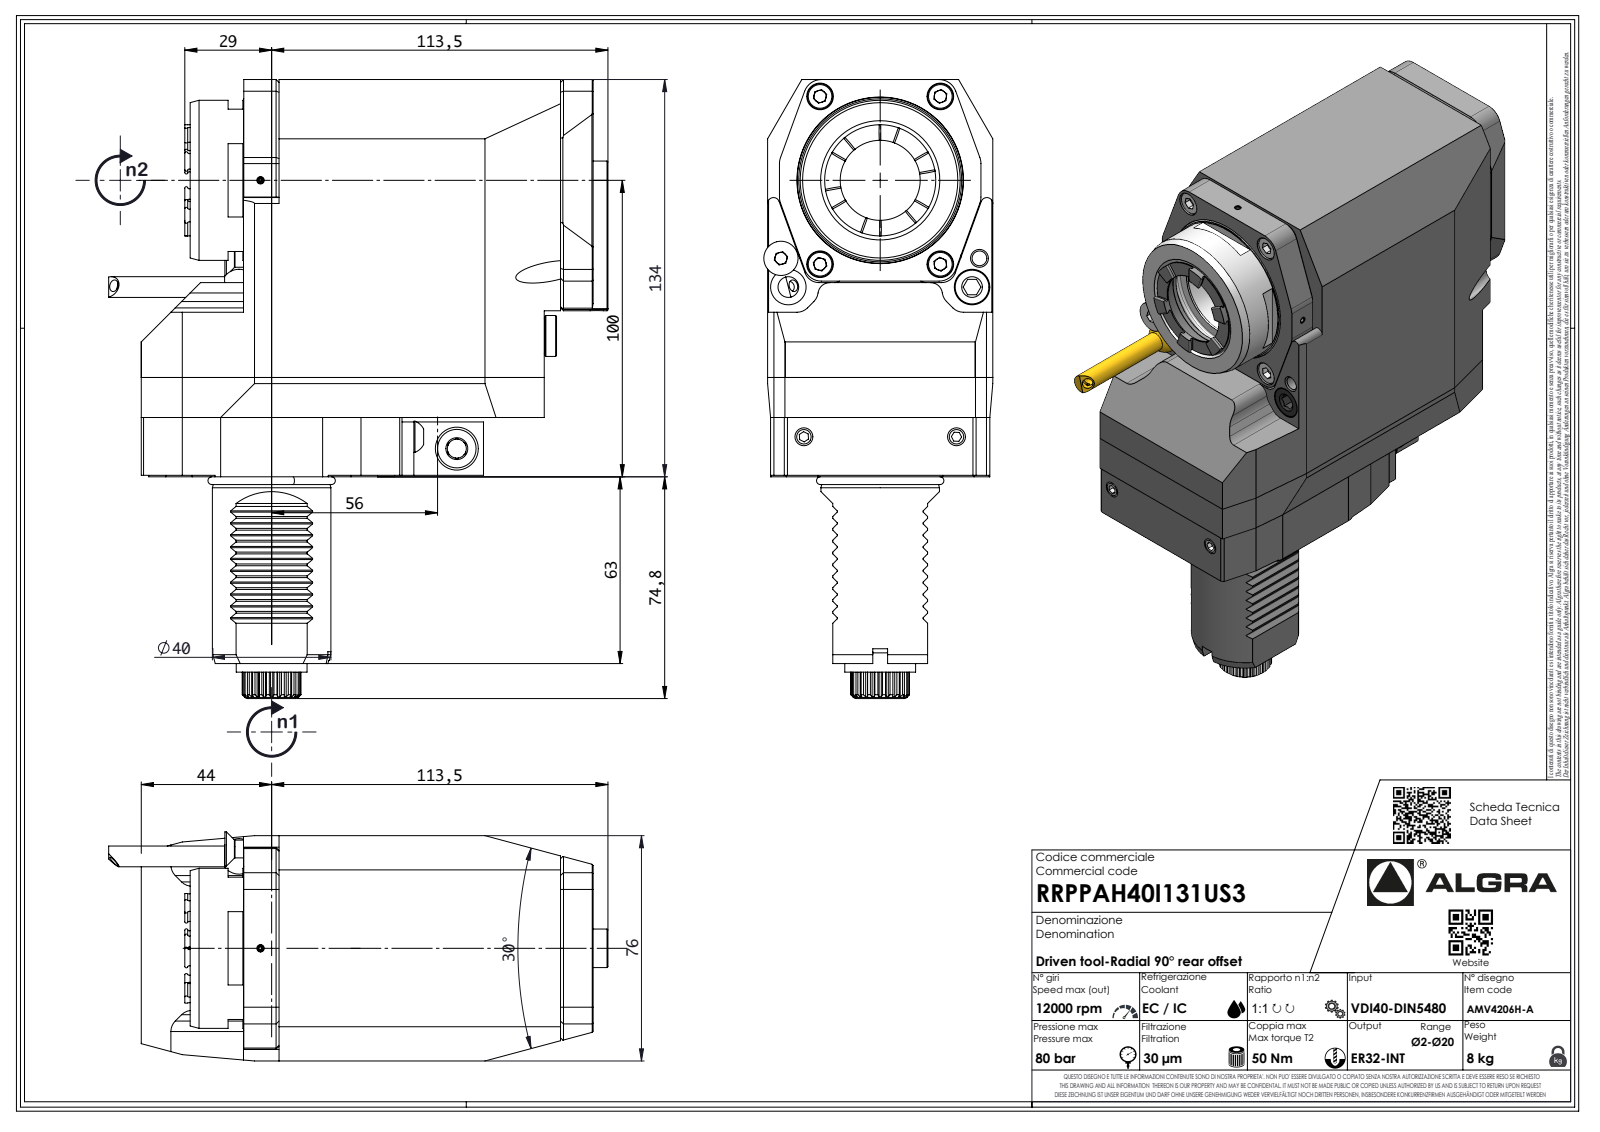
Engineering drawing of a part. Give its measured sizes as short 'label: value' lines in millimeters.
name: RRPPAH40I131US3
written by: SolidWorks 2023 (AUTOMOTIVE_DESIGN)
unit: mm
bodies: 2 solids, 790 faces (501 planar, 148 cylindrical, 141 other)
size: 208.8 × 157.5 × 76
volume: 1 258 000 mm³; area: 95 836 mm²
holes: 4× ⌀14, 2× ⌀5, 2× ⌀6.8, 1× ⌀2.05, 1× ⌀2.1, 1× ⌀6, 1× ⌀30.4
bosses: 1× ⌀54, 1× ⌀40, 1× ⌀38.7, 1× ⌀25.48, 1× ⌀23.9, 1× ⌀6.37, 1× ⌀1.7
rounds: 20× R0.3, 10× R6, 7× R0.33, 7× R0.52, 7× R3.7, 6× R5, 4× R3, 2× R0.5
face distances: 76, 16.5, 136, 114, 134, 20, 0.5, 152.5, 48, 18
hole spacings: 41.87, 30.94, 54, 55.86, 64, 83.74, 16.9
